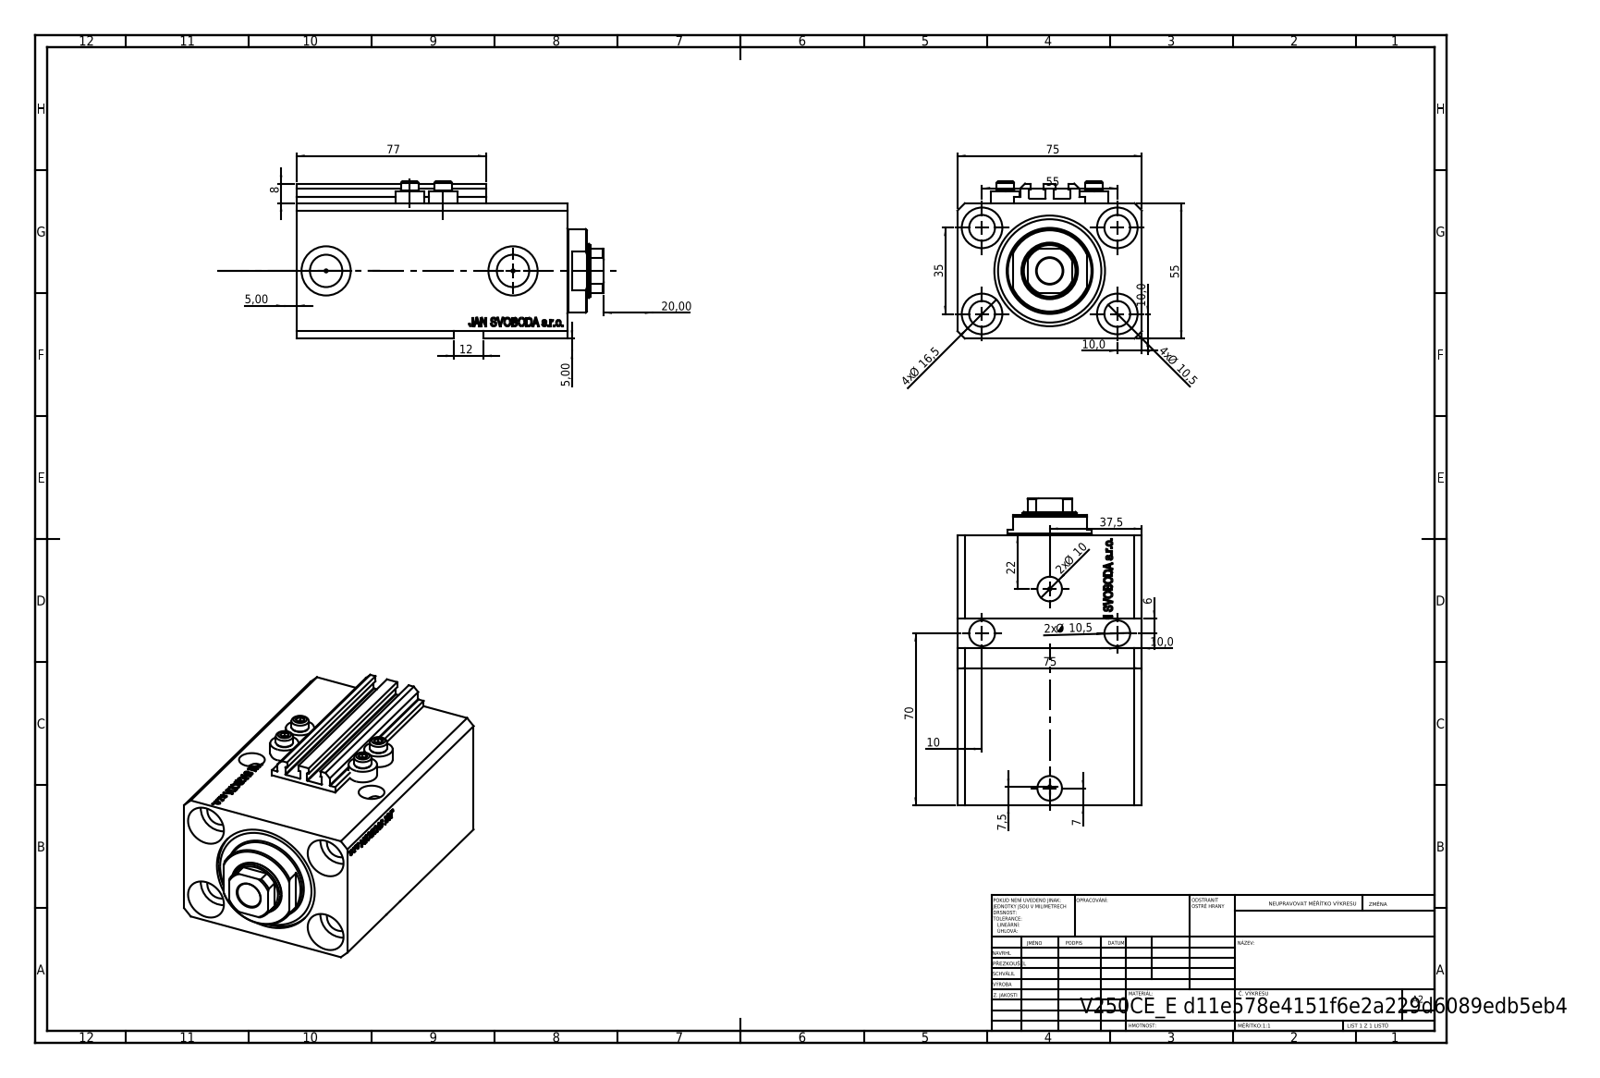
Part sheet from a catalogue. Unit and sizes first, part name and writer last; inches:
Units: inches
Overall size (bounding box): 4.917 × 2.953 × 2.52
Round holes (diameter × count): ⌀0.413 ×7, ⌀0.049 ×4, ⌀0.157 ×4, ⌀0.65 ×4, ⌀0.394 ×2, ⌀0.518 ×2, ⌀0.787 ×2, ⌀0.866 ×1, ⌀1.26 ×1, ⌀1.772 ×1
Round bosses / shafts (diameter × count): ⌀0.457 ×4, ⌀0.276 ×4, ⌀1.339 ×1
Partial cylindrical surfaces — rounded edges, fillets, slot ends (radius × count): R0.008 ×10, R0.413 ×1
Main face-to-face distances: 2.165, 2.953, 4.331, 3.264, 1.067, 0.118, 0.39, 2.874, 3.941, 2.244
Hole centre spacings: 1.283, 2.165, 0.535, 0.555, 1.016, 1.294, 1.324, 1.378
Volume: 23.66 in³ · Surface area: 149.9 in²
Bodies: 8 solids, 1064 faces (514 planar, 126 cylindrical, 424 other)
Part name (STEP PRODUCT): ALLEN BOLT V250CE; V250CE_E_Body; V250CE_VC_E; V250CE_C_VCP
STEP written by: SolidWorks 2019 (CONFIG_CONTROL_DESIGN)
